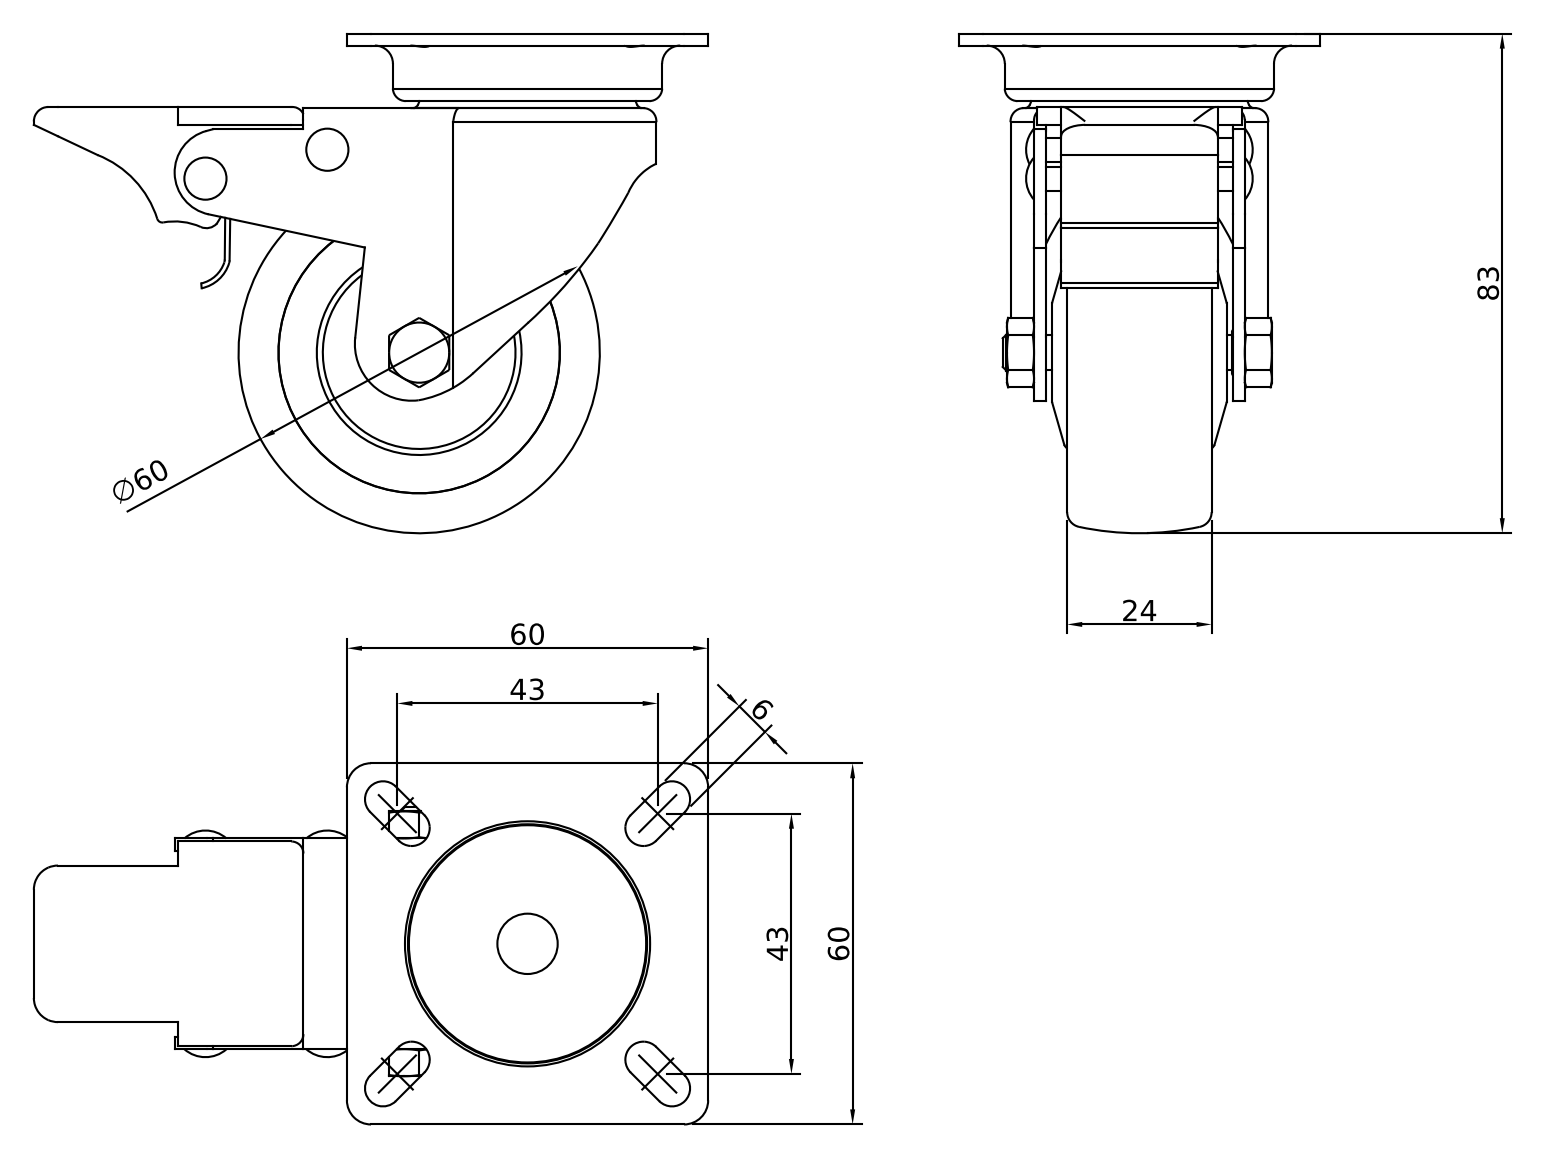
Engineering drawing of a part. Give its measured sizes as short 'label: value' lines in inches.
name: CRUST0000179; 440000025285; 440000025284; 440000025283 (+4 more)
written by: Autodesk Inventor 2022 (AUTOMOTIVE_DESIGN)
unit: in
bodies: 8 solids, 247 faces (99 planar, 77 cylindrical, 71 other)
size: 4.409 × 3.268 × 2.362
volume: 6.597 in³; area: 76.49 in²
holes: 1× ⌀0.194, 1× ⌀0.236, 1× ⌀0.315, 1× ⌀0.394, 1× ⌀1.22, 1× ⌀1.339, 1× ⌀1.339, 1× ⌀1.528, 1× ⌀1.603, 1× ⌀1.84
bosses: 2× ⌀0.157, 1× ⌀1.839, 1× ⌀1.761, 1× ⌀1.564, 1× ⌀1.26, 1× ⌀1.249, 1× ⌀1.102, 1× ⌀0.311
rounds: 8× R0.118, 6× R0.157, 5× R0.079, 2× R0.02, 1× R0.035, 1× R0.063, 1× R0.063, 1× R0.091
face distances: 0.079, 0.138, 1.161, 1.083, 0.039, 0.217, 1.299, 0.098, 0.059, 1.122
